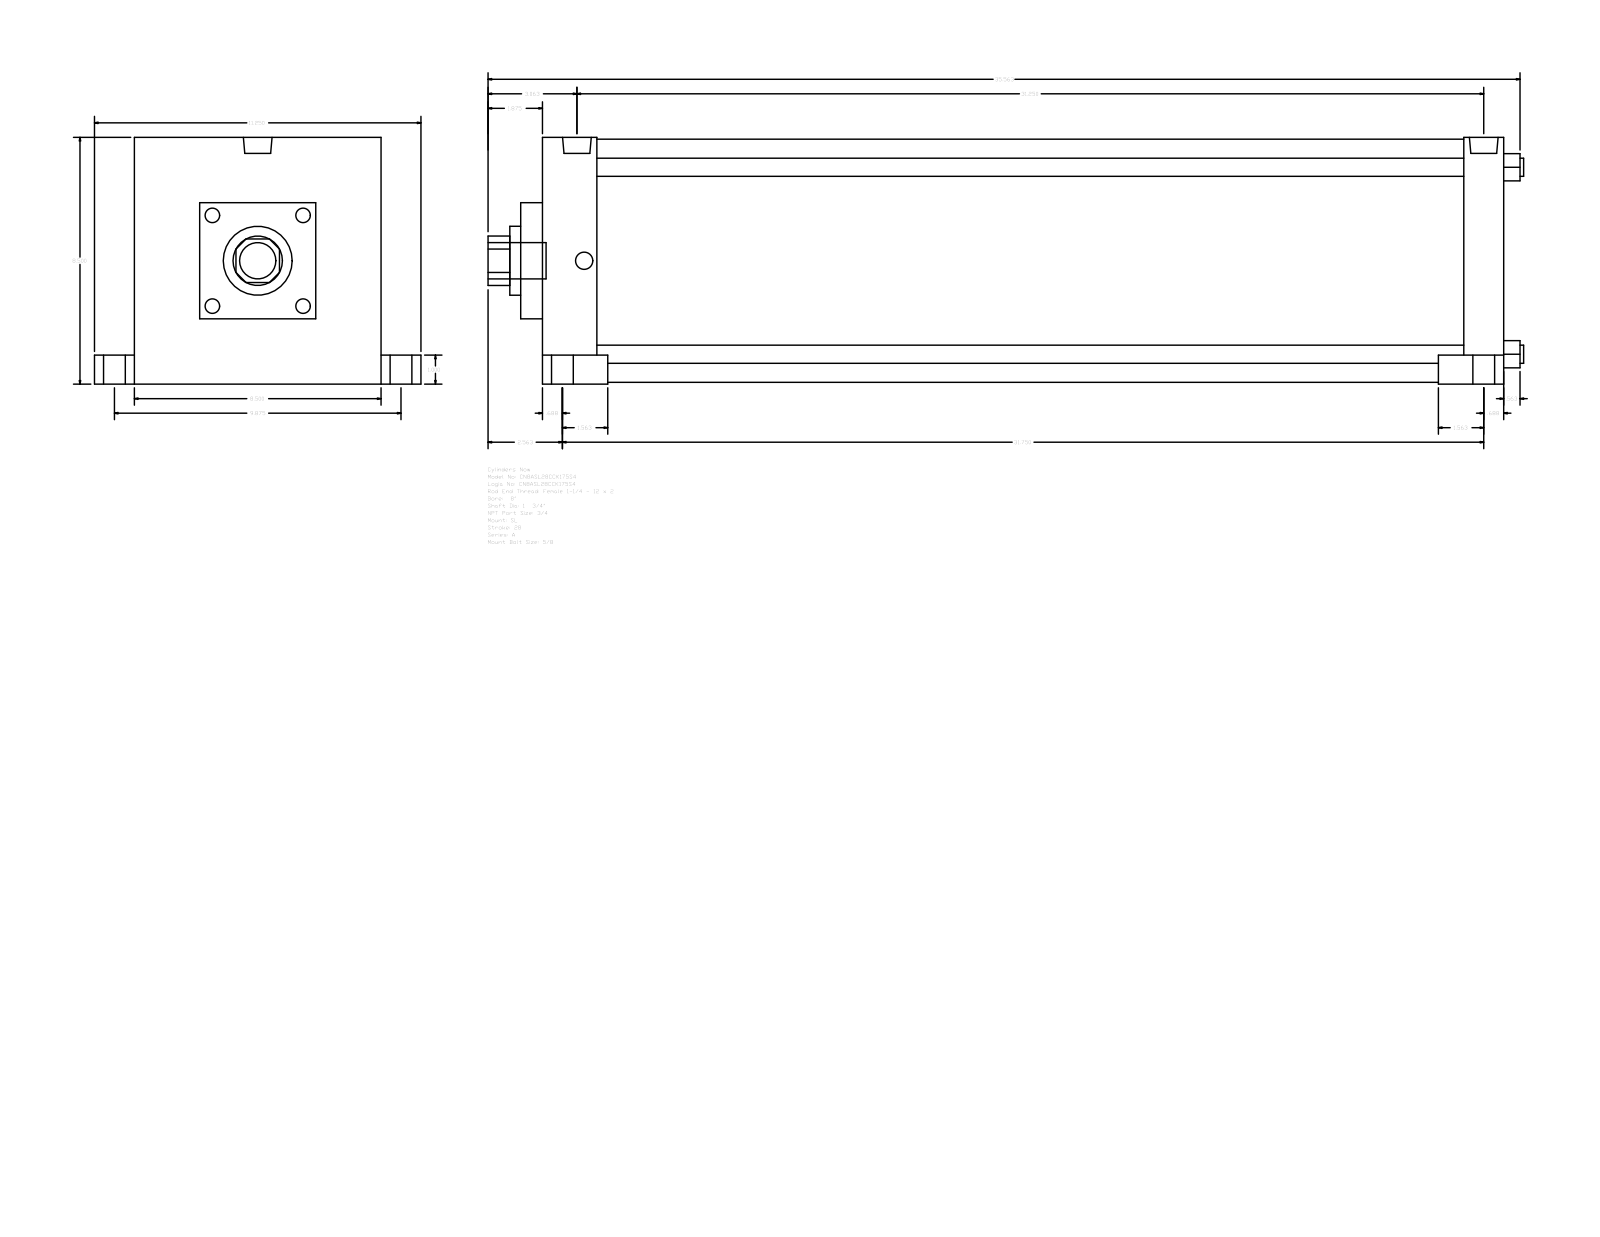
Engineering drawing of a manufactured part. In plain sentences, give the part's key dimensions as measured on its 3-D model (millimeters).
The part is named "A_SL__0800_1.75". Its 3-D file was written by "GSSL Pune (CONFIG_CONTROL_DESIGN)". It is 0 solids with 117 faces: 85 planar, 32 cylindrical and 0 other. Overall it measures 906.46 by 285.75 by 215.9 millimeters. Round holes: 4 of diameter 15.88, 1 of diameter 44.45, 1 of diameter 60.33, 1 of diameter 212.72. Round bosses or shafts: 4 of diameter 25.4, 4 of diameter 19.05, 4 of diameter 15.08, 2 of diameter 25.12, 1 of diameter 31.75. Partial cylindrical surfaces (rounded edges, fillets, slot ends): 1 of radius 21.63. The main face-to-face distances are 841.38, 215.9, 34.92, 47.63, 793.75, 806.46, 758.83, 57.15, 19.05, 158.75. The hole center spacings are 115.67, 163.58, 231.34.
